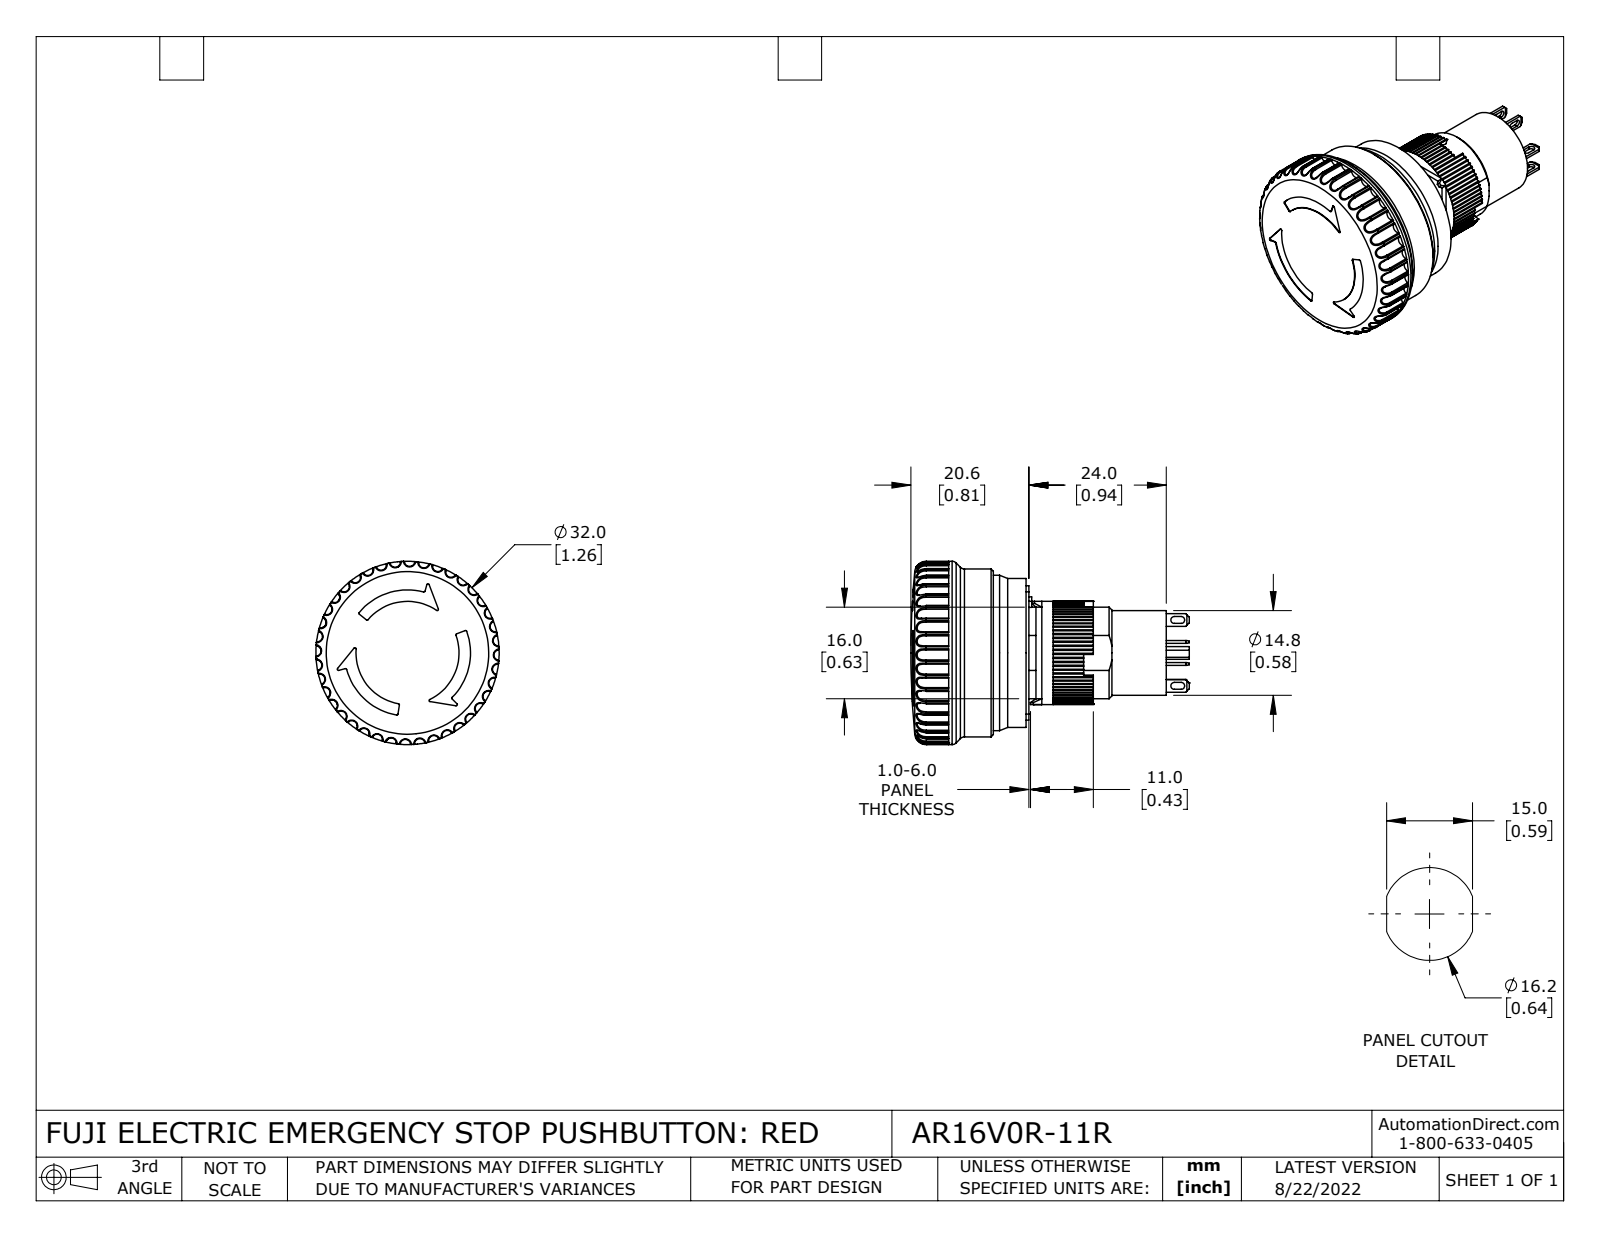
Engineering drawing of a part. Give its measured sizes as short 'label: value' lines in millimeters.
name: AR16V0R-11R
written by: SolidWorks 2021 (CONFIG_CONTROL_DESIGN)
unit: mm
bodies: 5 solids, 921 faces (488 planar, 359 cylindrical, 74 other)
size: 48.6 × 32 × 32
volume: 18 400 mm³; area: 8 742 mm²
holes: 1× ⌀14.8, 1× ⌀16, 1× ⌀27.2
bosses: 1× ⌀32, 1× ⌀29.3, 1× ⌀26, 1× ⌀21.8, 1× ⌀18, 1× ⌀6
rounds: 80× R0.2, 80× R0.3, 40× R0.9, 8× R0.5, 8× R0.6, 2× R1, 1× R0.8, 1× R2.9
face distances: 10.7, 13.5, 2.7, 1, 0.5, 1.8, 21.7, 12.4, 2.3, 1.2
